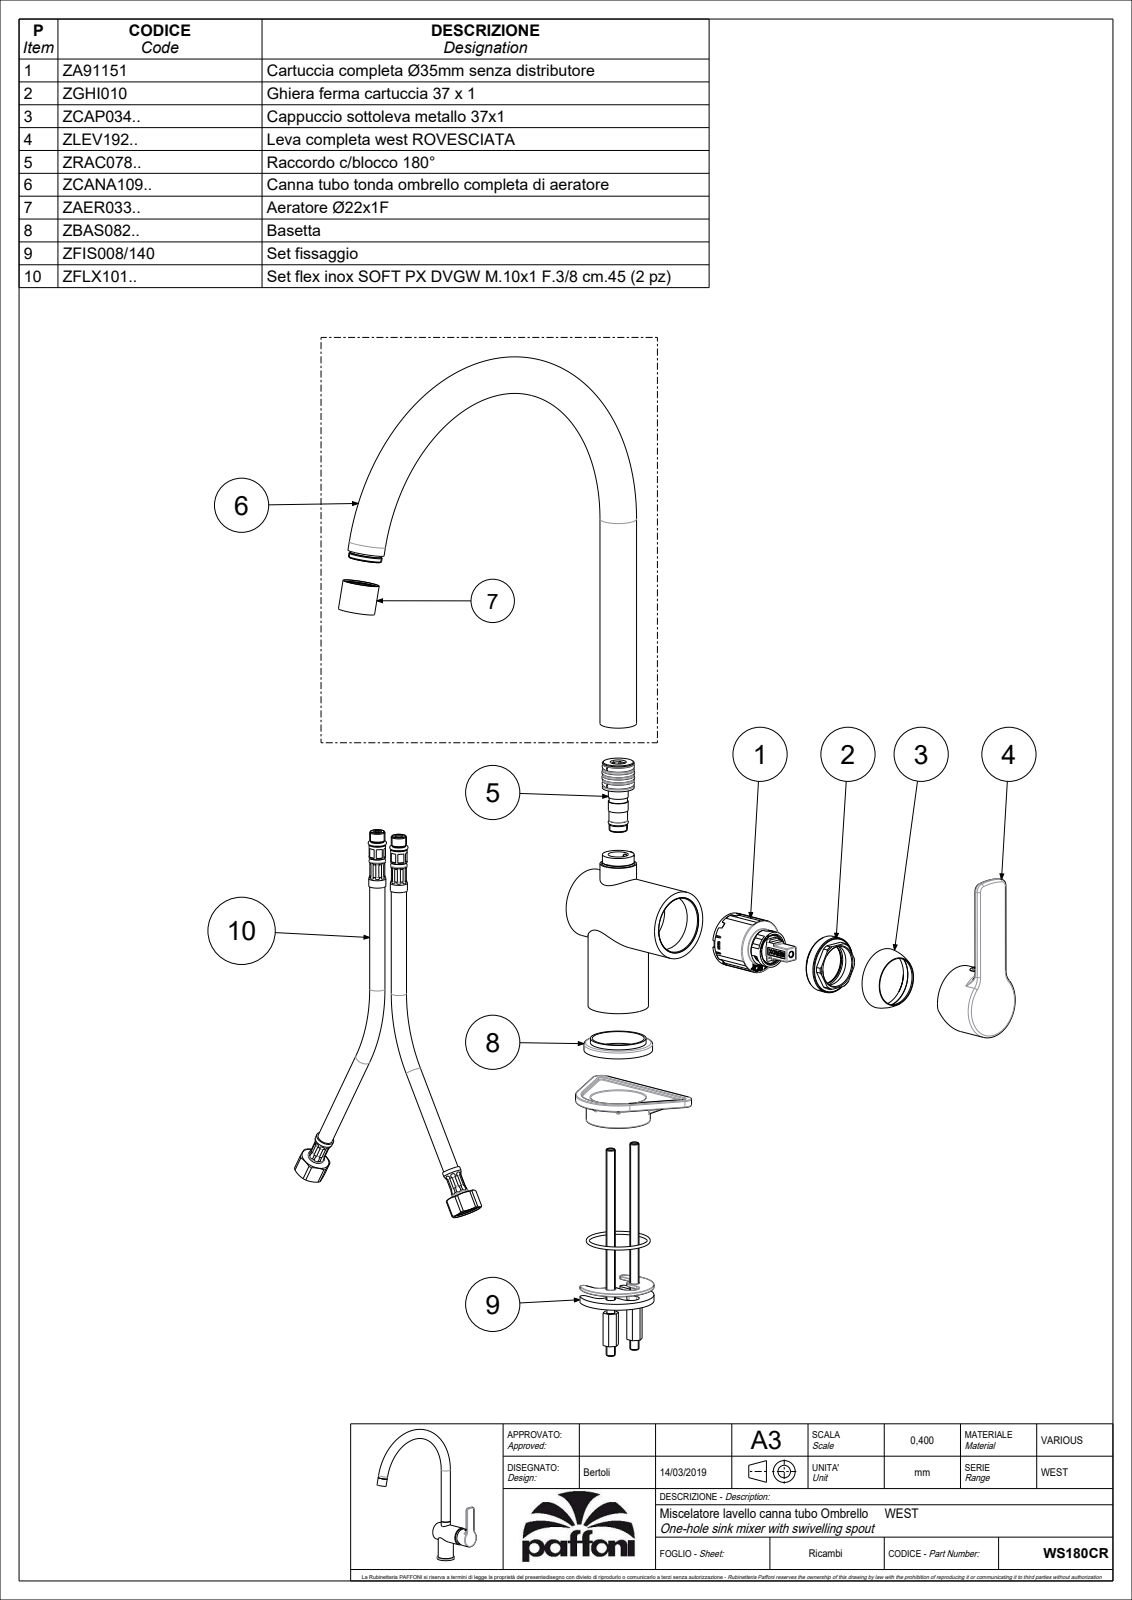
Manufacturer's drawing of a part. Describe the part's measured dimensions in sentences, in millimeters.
The part is named "WS180CR". Its 3-D file was written by "CREO PARAMETRIC BY PTC INC, 2020044 (CONFIG_CONTROL_DESIGN)". It is 3 solids with 3635 faces: 2536 planar, 599 cylindrical and 500 other. Overall it measures 370.9 by 272.52 by 118.83 millimeters. Its volume is 200 881 cubic millimeters and its surface area 151 741 square millimeters. Round holes: 9 of diameter 2.5, 3 of diameter 5.5, 3 of diameter 6, 3 of diameter 11, 2 of diameter 7, 2 of diameter 9, 2 of diameter 36, 1 of diameter 3, 1 of diameter 3.3, 1 of diameter 3.4, 1 of diameter 3.5, 1 of diameter 4. Round bosses or shafts: 2 of diameter 24, 2 of diameter 19.5, 2 of diameter 4, 1 of diameter 45, 1 of diameter 44.7, 1 of diameter 43, 1 of diameter 39.6, 1 of diameter 38.5. Partial cylindrical surfaces (rounded edges, fillets, slot ends): 91 of radius 0.5, 20 of radius 0.3, 16 of radius 0.2, 12 of radius 24.3, 9 of radius 1.5, 6 of radius 1.7, 6 of radius 5, 4 of radius 3. The main face-to-face distances are 4.5, 1.5, 3.5, 70.8, 2, 8, 0.5, 11.5, 4.46, 3. The hole center spacings are 8.9, 4.61, 17.65, 5.06, 8.49, 9.43, 9.6, 10.59.
